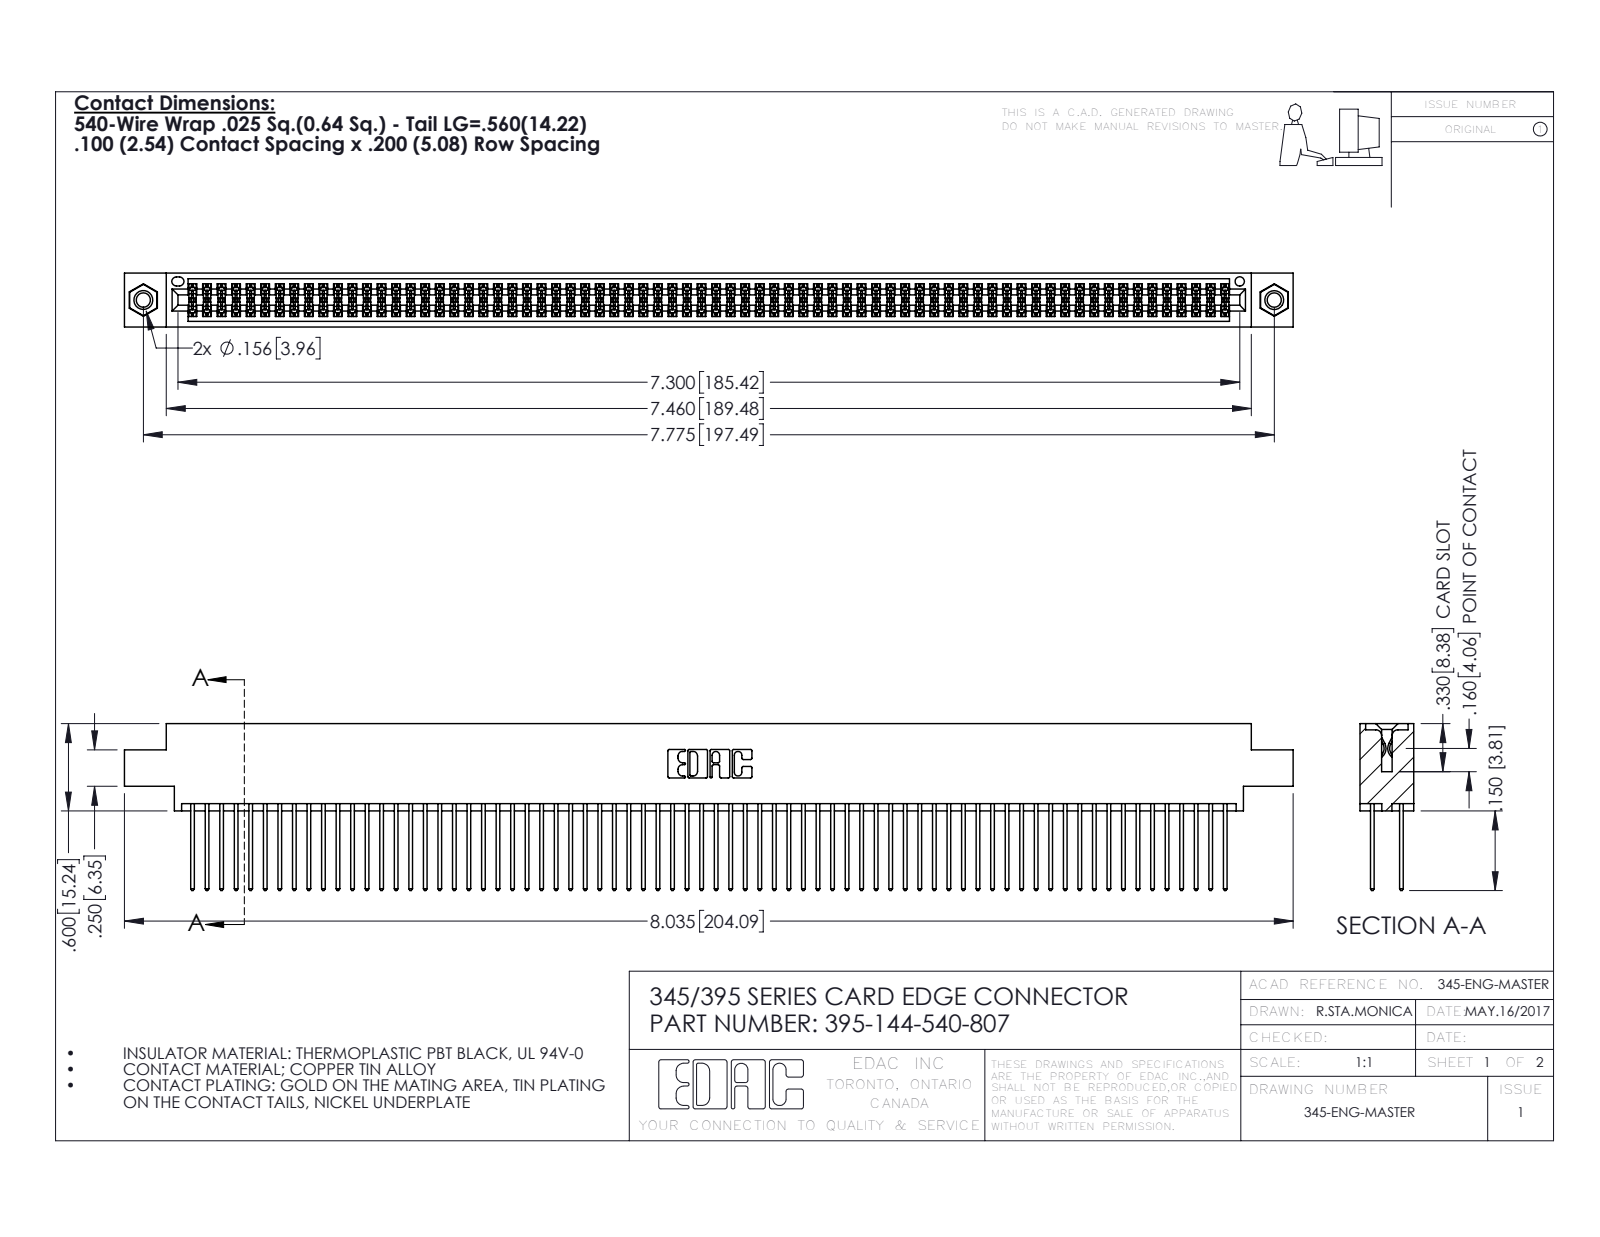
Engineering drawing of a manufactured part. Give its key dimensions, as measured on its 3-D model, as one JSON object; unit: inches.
{"part_name": "345 Part_0.170 Offset - 0.156 Dia-TI; 345-250-001_345-250-005-103; 395-144-540-807; 345-292-001_345-293-140", "step_written_by": "SolidWorks 2016 (CONFIG_CONTROL_DESIGN)", "units": "inches", "bodies": {"solids": 147, "faces": 7390, "planar": 4868, "cylindrical": 2506, "other": 16}, "overall_size": [8.035, 1.147, 0.37], "volume_in3": 1.252, "surface_area_in2": 52.11, "round_holes": [[0.098, 2], [0.125, 2], [0.156, 2], [0.064, 1]], "round_bosses_or_shafts": [[0.155, 2]], "partial_cylinders_radius": [[0.006, 216], [0.01, 144], [0.01, 22], [0.007, 6], [0.031, 6], [0.026, 3], [0.014, 2], [0.019, 2]], "face_to_face_distances": [0.072, 0.298, 0.2, 0.098, 0.272, 0.025, 0.37, 0.225, 0.175, 0.149], "hole_center_spacings": [0.27, 7.539, 7.775]}
